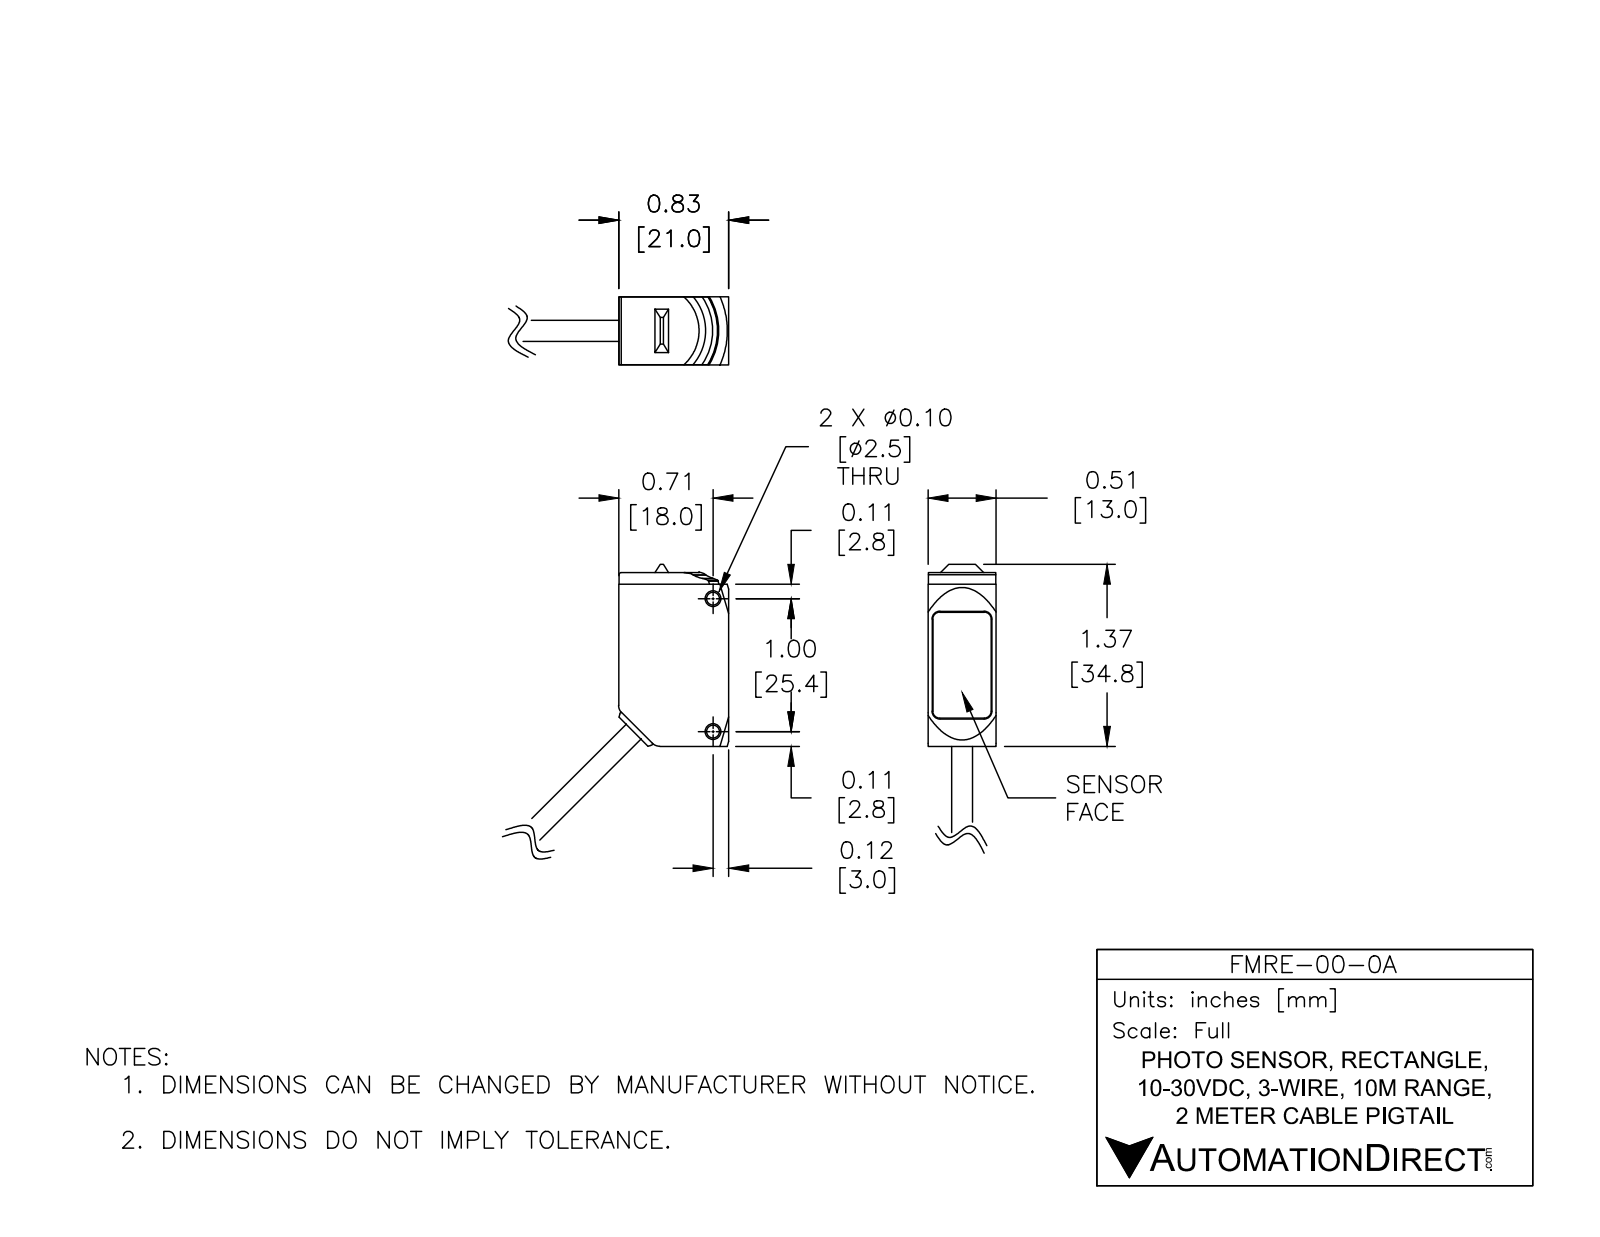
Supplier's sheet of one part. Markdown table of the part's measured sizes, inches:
| quantity | value |
| --- | --- |
| part name | FMRE-00-0A |
| STEP written by | SolidWorks 2017 (AUTOMOTIVE_DESIGN) |
| units | inches |
| bodies | 1 solid, 104 faces (44 planar, 39 cylindrical, 21 other) |
| overall size | 2.084 × 1.541 × 0.512 |
| volume | 0.541 in³ |
| surface area | 5.337 in² |
| round holes (diameter × count) | 0.097 × 2 |
| round bosses / shafts (diameter × count) | 0.157 × 1 |
| partial cylindrical surfaces (radius × count) | 0.018 × 7, 0.02 × 7, 0.051 × 4, 0.059 × 4, 0.079 × 2, 0.094 × 2, 0.096 × 2, 0.65 × 2 |
| main face-to-face distances | 0.512, 0.827, 1.307, 0.035, 0.51, 0.037, 0.474, 0.472, 0.031, 0.48 |
| hole center spacings | 1 |
